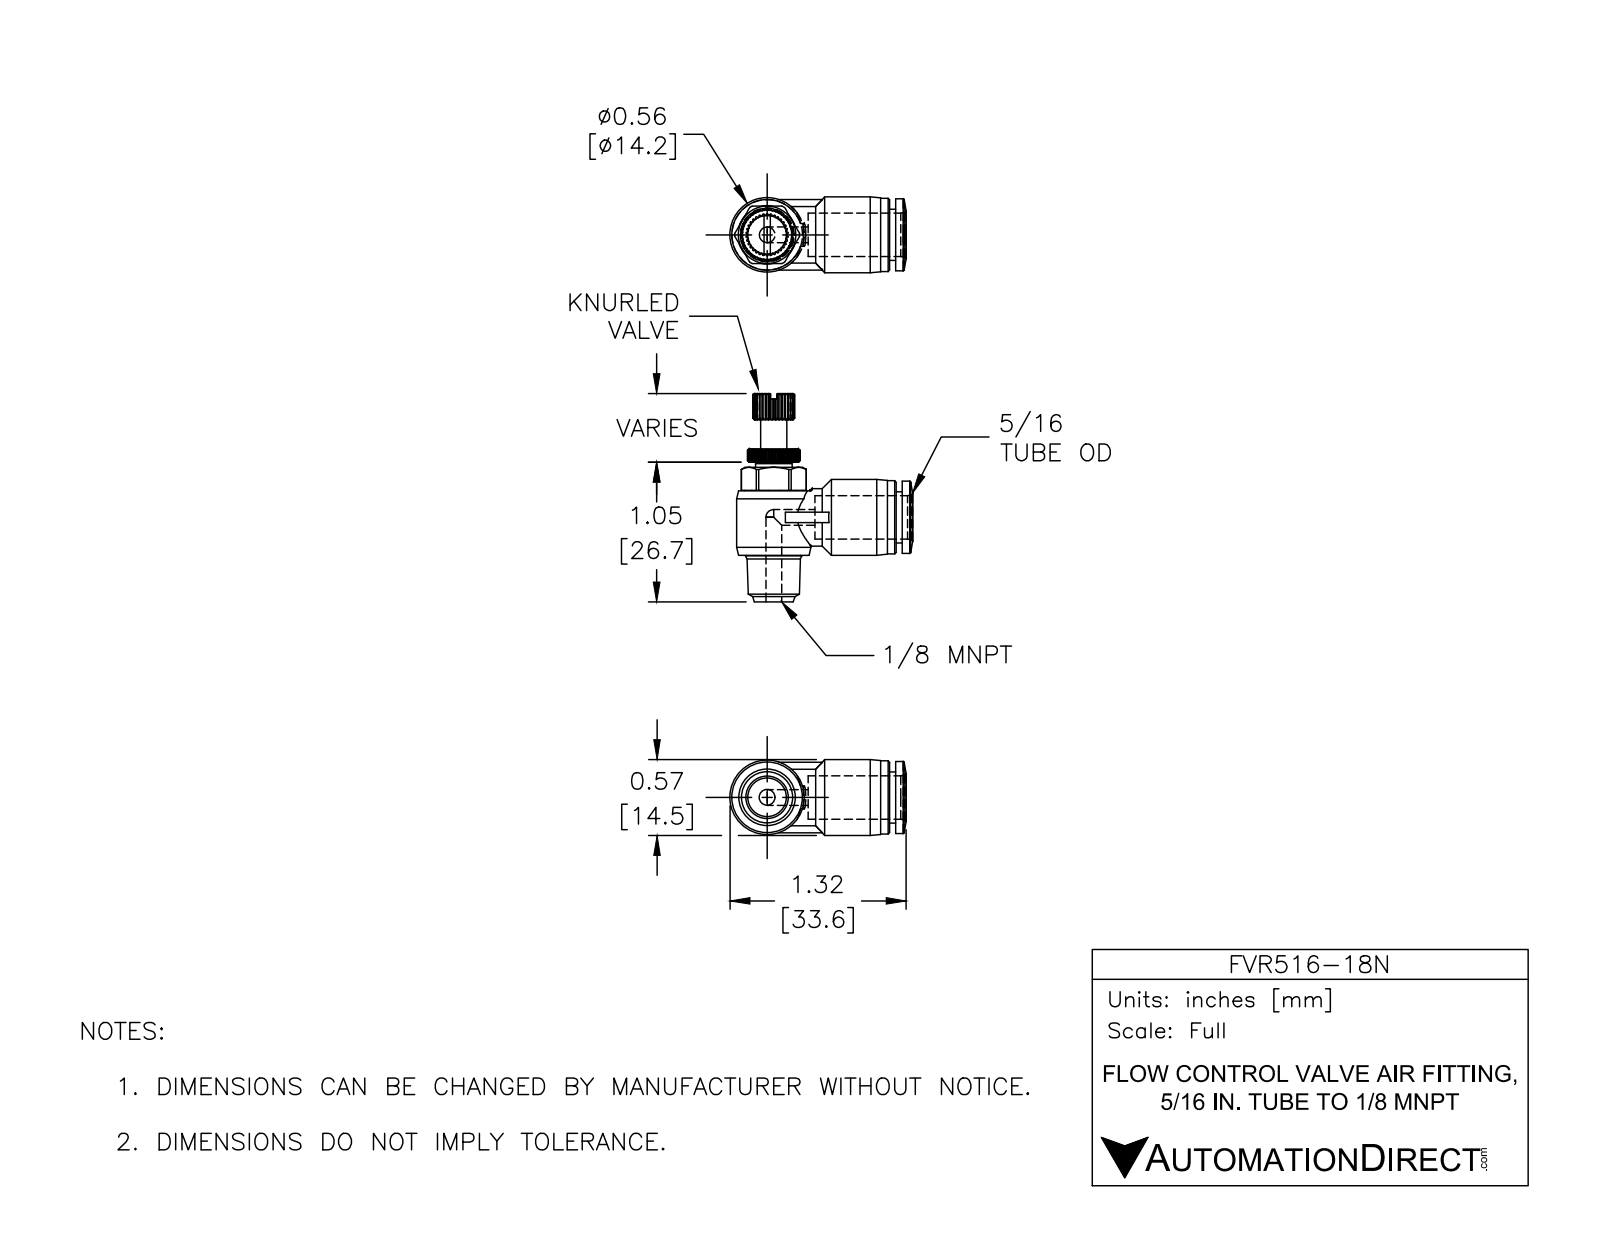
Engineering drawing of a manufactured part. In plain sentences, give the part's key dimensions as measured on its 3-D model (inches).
The part is named "FVR516-18N". Its 3-D file was written by "SolidWorks 2015 (CONFIG_CONTROL_DESIGN)". It is 1 solid with 508 faces: 199 planar, 113 cylindrical and 196 other. Overall it measures 1.567 by 1.325 by 0.571 inches. Its volume is 0.326 cubic inches and its surface area 5.553 square inches. Round holes: 2 of diameter 0.118, 1 of diameter 0.327. Round bosses or shafts: 1 of diameter 0.571, 1 of diameter 0.559, 1 of diameter 0.551, 1 of diameter 0.543, 1 of diameter 0.441, 1 of diameter 0.433, 1 of diameter 0.406, 1 of diameter 0.386. Partial cylindrical surfaces (rounded edges, fillets, slot ends): 1 of radius 0.157, 1 of radius 0.197, 1 of radius 0.244. The main face-to-face distances are 0.433, 0.045, 0.661, 0.206, 0.799, 0.138, 0.612, 0.657, 0.039, 0.484.
